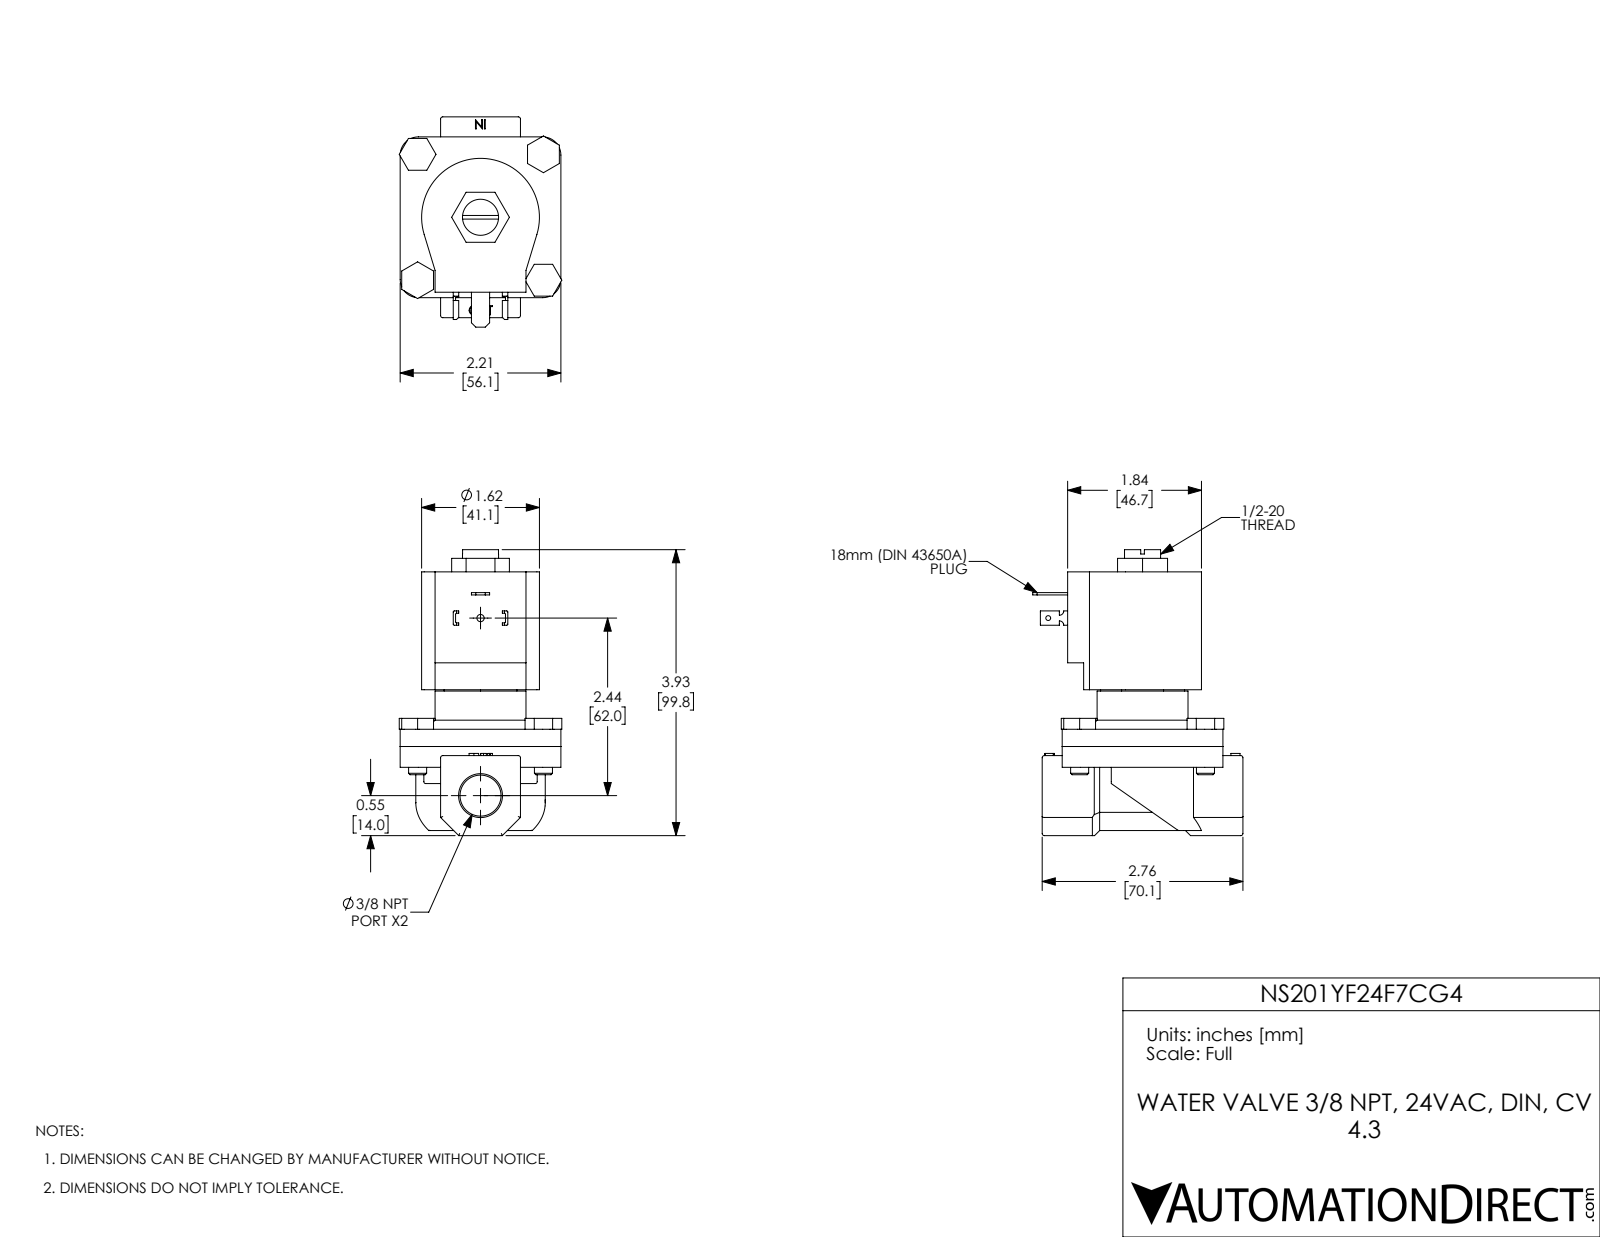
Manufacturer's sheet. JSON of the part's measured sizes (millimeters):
{"part_name": "NS201YF24F7CG4", "step_written_by": "SolidWorks 2017 (AUTOMOTIVE_DESIGN)", "units": "millimeters", "bodies": {"solids": 11, "faces": 330, "planar": 196, "cylindrical": 99, "other": 35}, "overall_size": [99.8, 73.4, 56.8], "volume_mm3": 164000, "surface_area_mm2": 40530, "round_holes": [[6.4, 4], [1.7, 1], [2.5, 1], [12.6, 1], [13, 1], [14.3, 1], [29.3, 1]], "round_bosses_or_shafts": [[6.3, 4], [31.8, 1]], "partial_cylinders_radius": [[0.8, 15], [0.4, 8], [6.4, 4], [1.5, 2], [20.6, 1], [22.6, 1]], "face_to_face_distances": [6, 6, 61, 61, 54.9, 14.1, 42, 7.3, 7.3, 13.3], "hole_center_spacings": [31.1, 43.9, 62.1, 62]}
